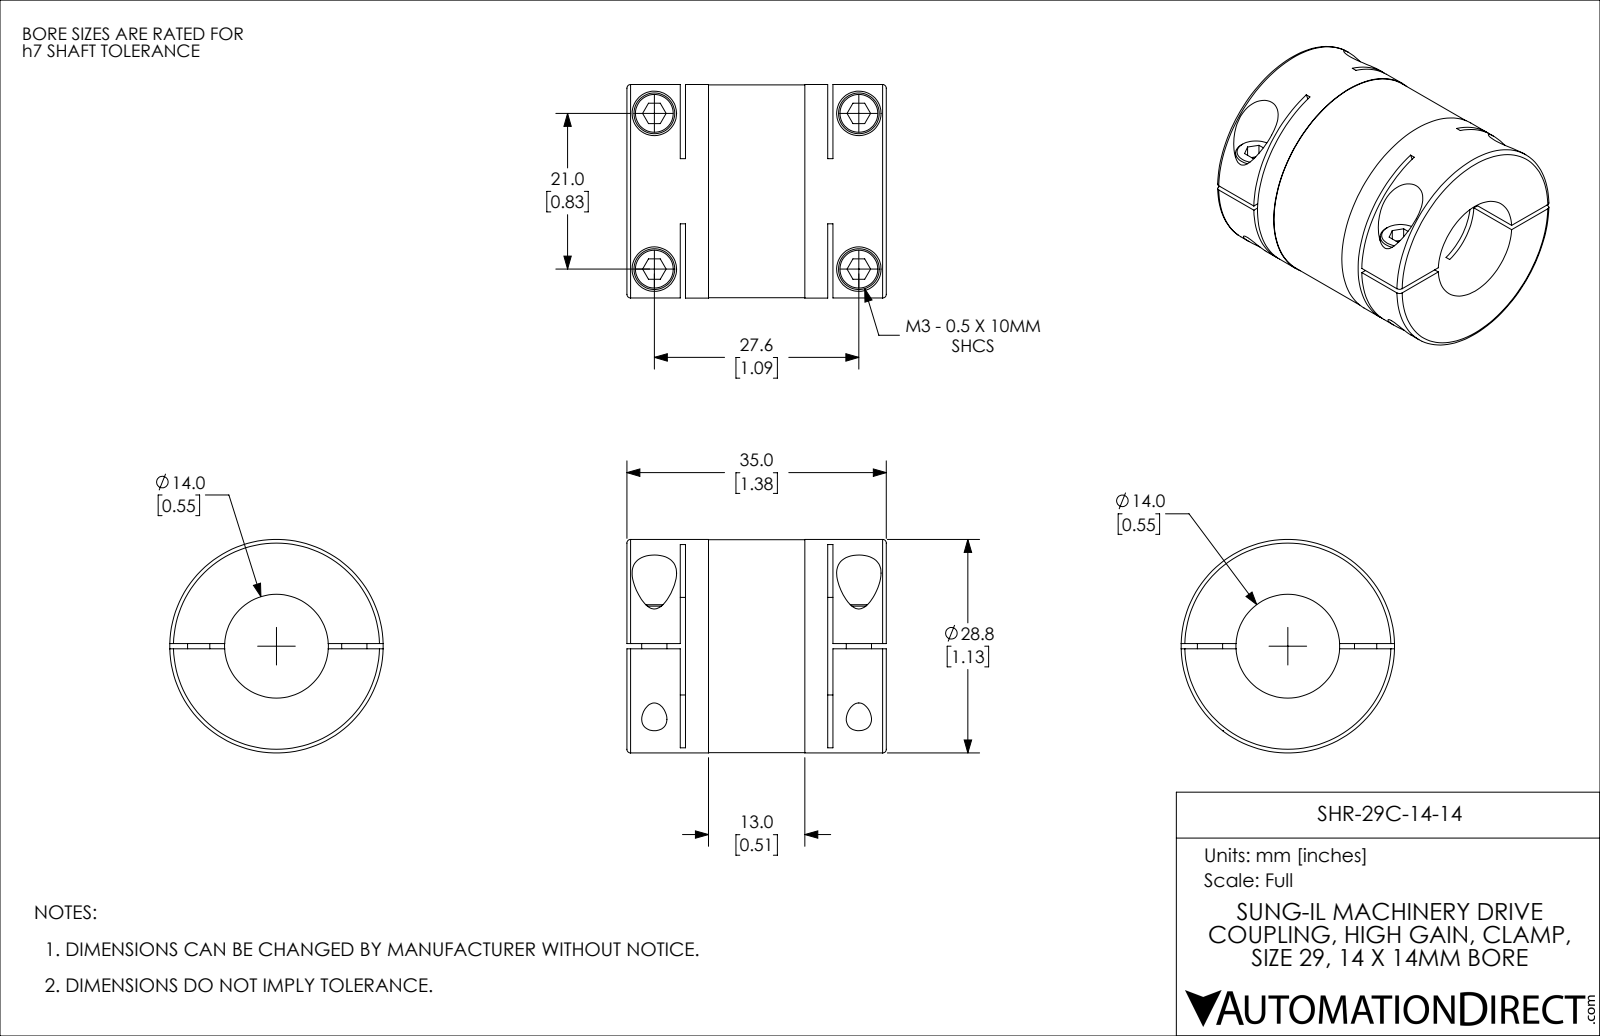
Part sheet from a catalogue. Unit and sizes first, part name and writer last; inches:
Units: inches
Overall size (bounding box): 1.378 × 1.134 × 1.134
Round holes (diameter × count): ⌀0.134 ×4, ⌀0.236 ×4, ⌀0.551 ×1, ⌀0.63 ×1
Round bosses / shafts (diameter × count): ⌀0.217 ×4, ⌀0.118 ×2, ⌀1.134 ×1, ⌀1.13 ×1
Partial cylindrical surfaces — rounded edges, fillets, slot ends (radius × count): R1.476 ×2
Main face-to-face distances: 0.028, 0.311, 1.067, 0.283, 1.094, 0.783, 1.378, 0.756, 0.811, 0.433
Hole centre spacings: 0.827, 1.087, 1.365
Volume: 0.938 in³ · Surface area: 13.61 in²
Bodies: 1 solid, 145 faces (70 planar, 57 cylindrical, 18 other)
Part name (STEP PRODUCT): SHR-29C-14-14
STEP written by: SolidWorks 2021 (CONFIG_CONTROL_DESIGN)
